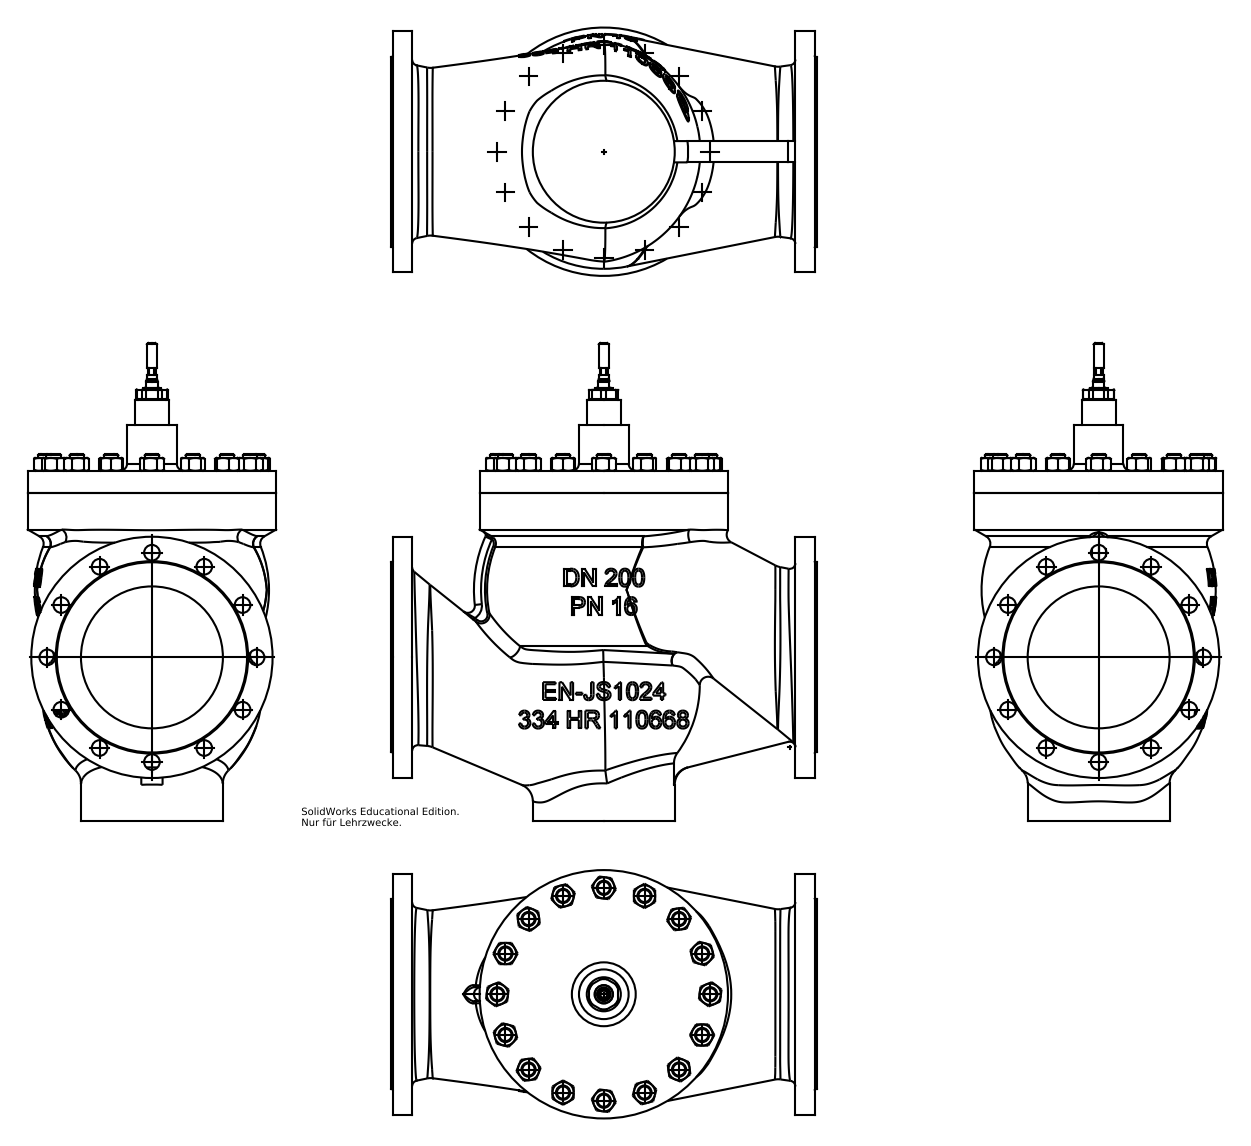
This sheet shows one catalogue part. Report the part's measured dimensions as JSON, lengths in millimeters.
{"part_name": "BR225 DN200 XXX PN16 for MC_STEP (Defeature)", "step_written_by": "SolidWorks 2014 (AUTOMOTIVE_DESIGN)", "units": "millimeters", "bodies": {"solids": 1, "faces": 1055, "planar": 325, "cylindrical": 151, "other": 579}, "overall_size": [674, 600, 350], "volume_mm3": 51830000, "surface_area_mm2": 1289000, "round_holes": [[22, 12], [200, 1], [260.2, 1]], "round_bosses_or_shafts": [[20, 16], [350, 1], [340, 1], [268, 1], [259.8, 1], [200, 1], [70, 1], [48, 1]], "partial_cylinders_radius": [[8, 1], [22, 1]], "face_to_face_distances": [30, 20, 560, 7, 27, 567, 587, 3, 10, 570], "hole_center_spacings": [147.5, 76.35, 208.6, 255.48, 284.95, 295]}
